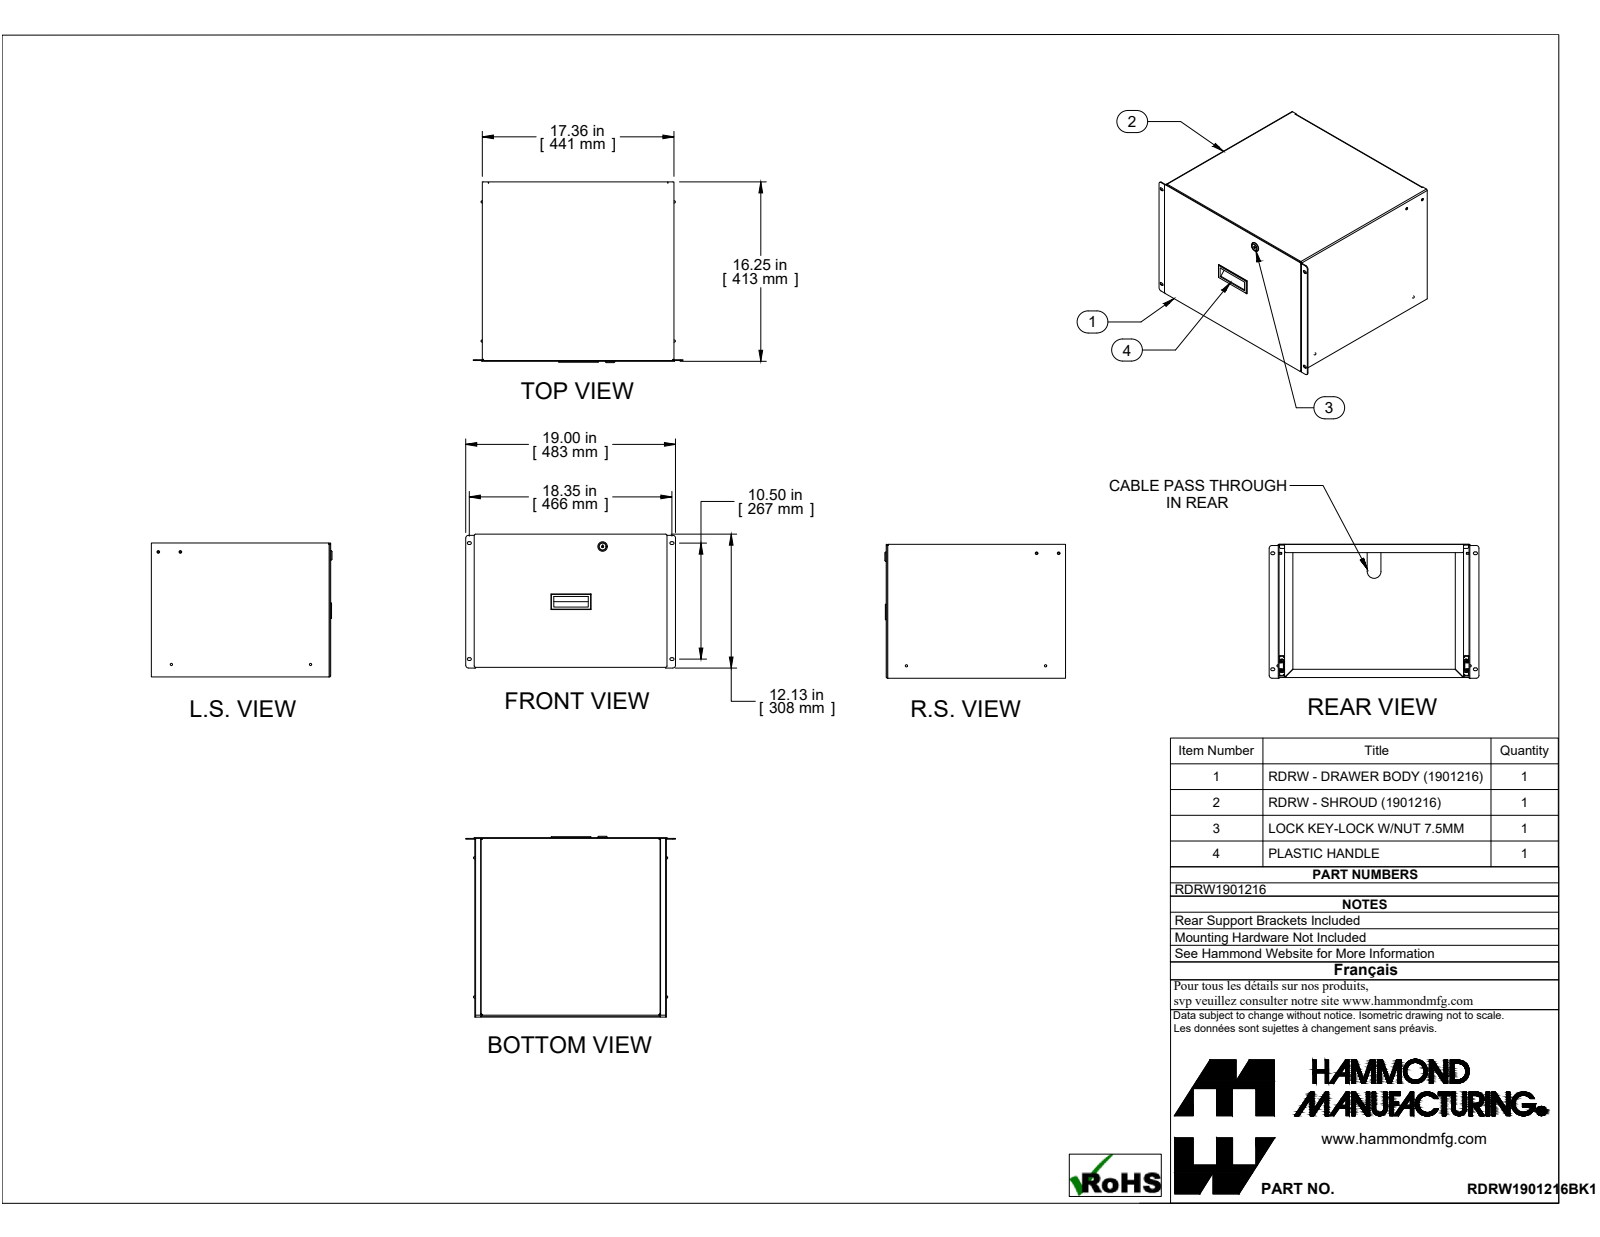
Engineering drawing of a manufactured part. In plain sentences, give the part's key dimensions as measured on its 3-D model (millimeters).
The part is named "RDRW1901216BK1". Its 3-D file was written by "SolidWorks 2019 (CONFIG_CONTROL_DESIGN)". It is 24 solids with 682 faces: 376 planar, 264 cylindrical and 42 other. Overall it measures 482.6 by 415.6 by 308 millimeters. Its volume is 1 944 000 cubic millimeters and its surface area 2 561 000 square millimeters. Round holes: 6 of diameter 4.5, 4 of diameter 4, 4 of diameter 4.6, 4 of diameter 6.4, 3 of diameter 4.4, 2 of diameter 4.1, 1 of diameter 3.9, 1 of diameter 5. Round bosses or shafts: 2 of diameter 6, 2 of diameter 4.2, 1 of diameter 22, 1 of diameter 15.9, 1 of diameter 13.9, 1 of diameter 8.5. Partial cylindrical surfaces (rounded edges, fillets, slot ends): 52 of radius 2.2, 40 of radius 0.7, 16 of radius 1.3, 16 of radius 3.2, 8 of radius 0.6, 8 of radius 1.8, 6 of radius 0.9, 6 of radius 2.5. The main face-to-face distances are 1.8, 1.2, 424.5, 12.7, 14.5, 426.3, 439, 15.7, 425.1, 13.9. The hole center spacings are 9.7, 320, 9.1, 15.8, 18.8, 25.5, 32, 34.6.
